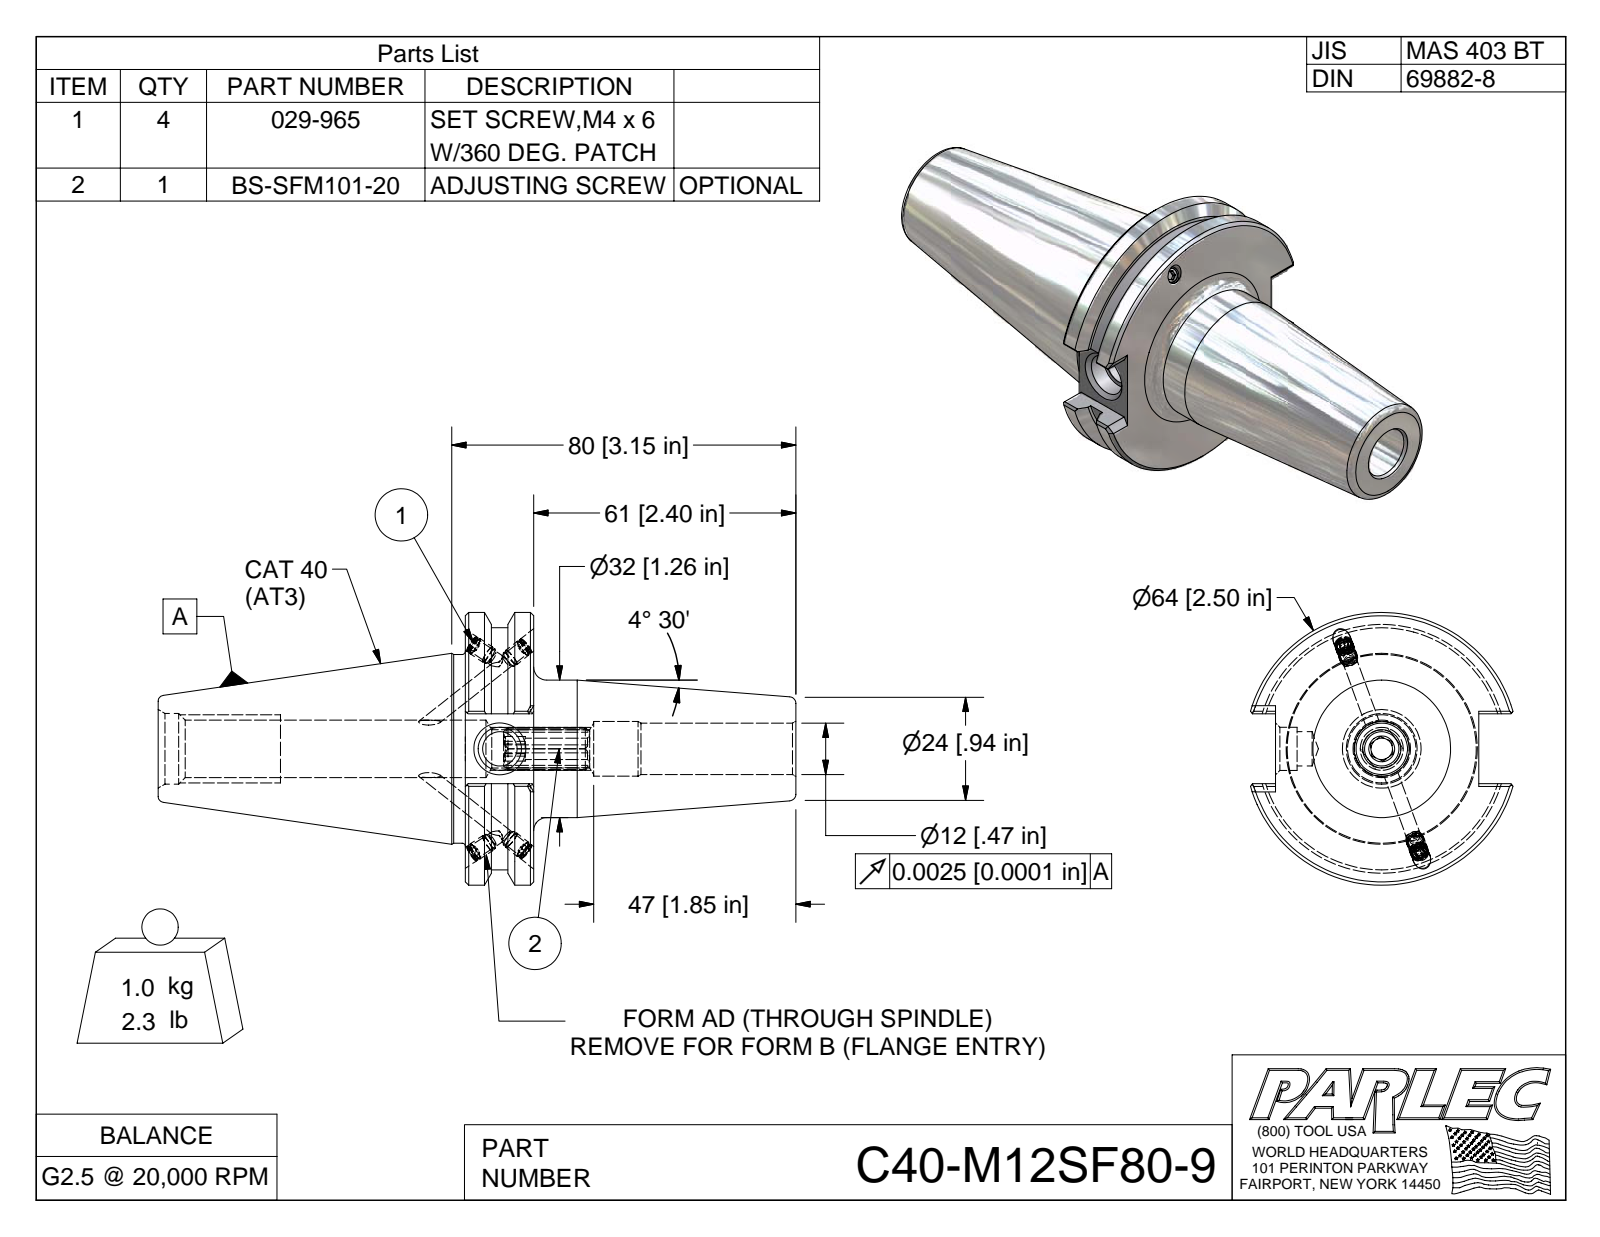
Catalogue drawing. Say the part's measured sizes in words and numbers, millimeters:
The part is named "C40-M12SF80-9; C40BC-M12SF80-9-1; 029-965; BS-SFM101-20". Its 3-D file was written by "Autodesk Inventor 2009 (AUTOMOTIVE_DESIGN)". It is 6 solids with 172 faces: 87 planar, 32 cylindrical and 53 other. Overall it measures 148.3 by 63.5 by 61 millimeters. Its volume is 135 200 cubic millimeters and its surface area 29 540 square millimeters. Round holes: 4 of diameter 3.3, 4 of diameter 4.1, 1 of diameter 12, 1 of diameter 12.7. Round bosses or shafts: 4 of diameter 4.2, 4 of diameter 4, 1 of diameter 63.5, 1 of diameter 56.4, 1 of diameter 43.9, 1 of diameter 32. Partial cylindrical surfaces (rounded edges, fillets, slot ends): 1 of radius 5. The main face-to-face distances are 15.9, 76.8, 61, 16.3, 47.2, 71.4, 87.3, 148.3, 8, 81.3.
